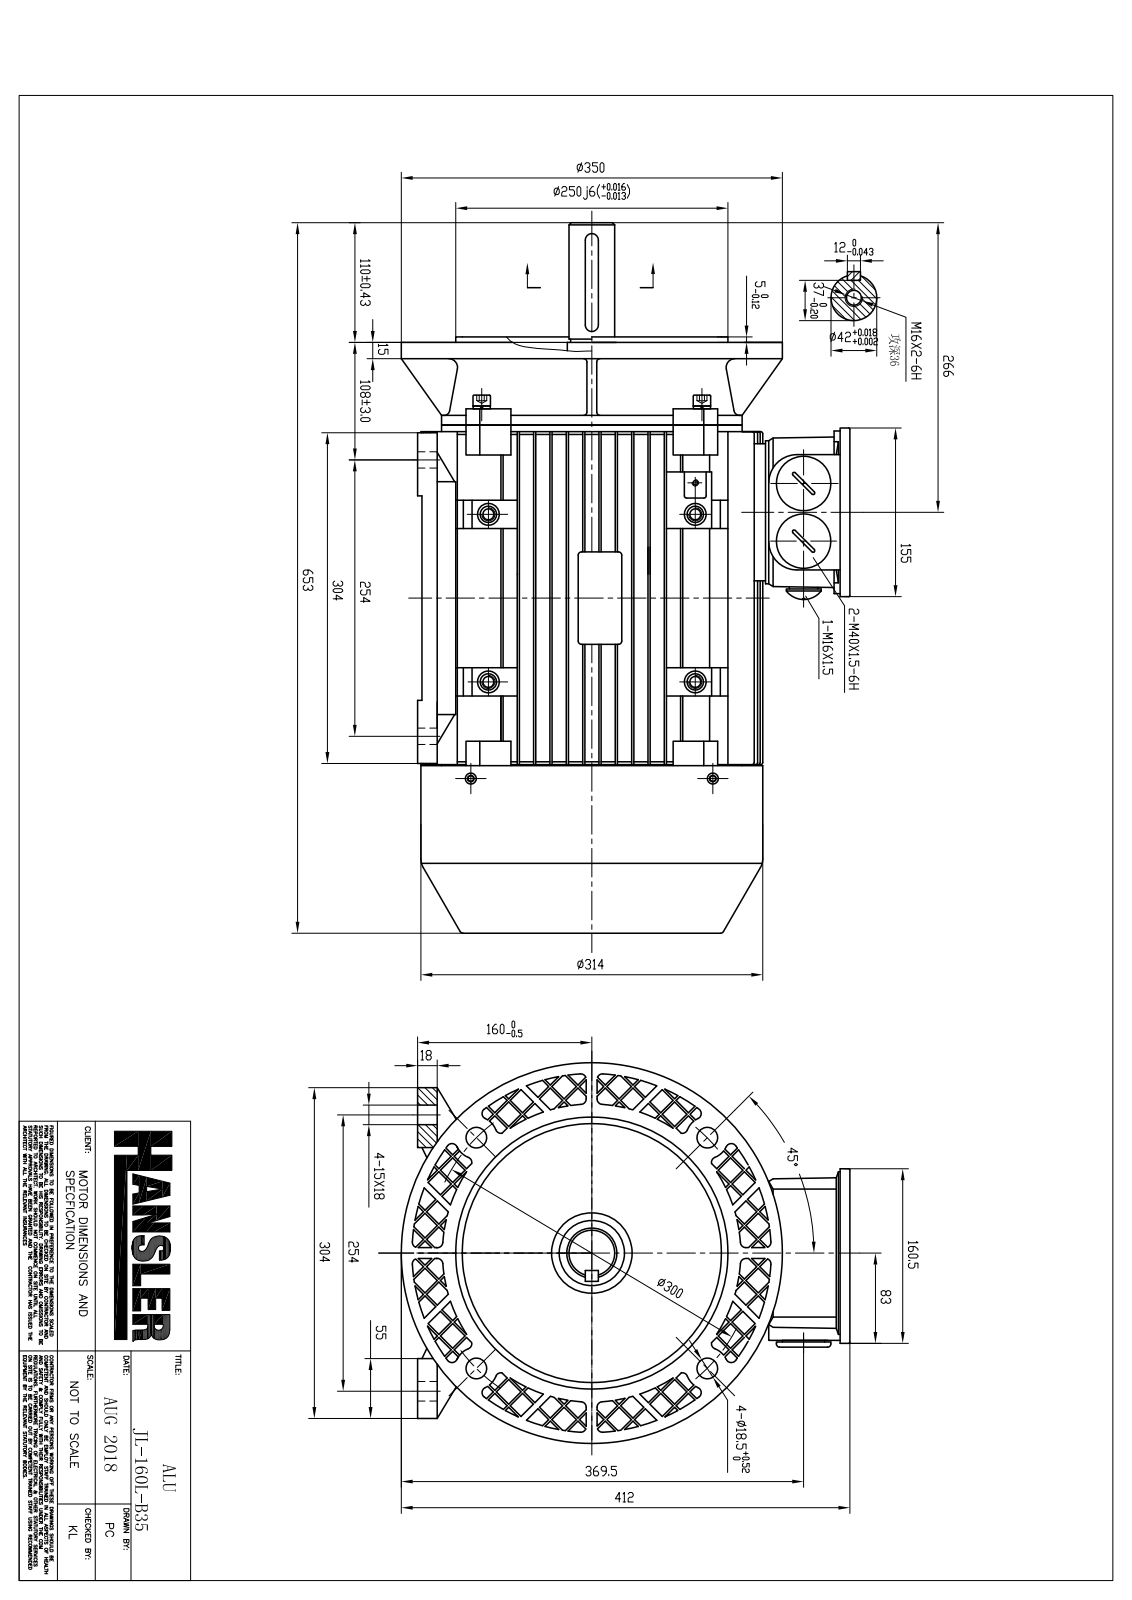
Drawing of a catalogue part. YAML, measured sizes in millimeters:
part_name: "JL-160L-B35"
step_written_by: "SIEMENS PLM Software NX 12.0 (AP203_CONFIGURATION_CONTROLLED_3D_DESIGN_OF_MECHANICAL_PARTS_AND_ASSEMBLIES_MIM_LF)"
units: millimeters
bodies: {solids: 67, faces: 8639, planar: 3998, cylindrical: 2180, other: 2461}
overall_size: [650.92, 417.7, 350]
volume: 7949000
surface_area: 2940000
round_holes:
  - {diameter: 5, count: 28}
  - {diameter: 4.12, count: 12}
  - {diameter: 8.39, count: 8}
  - {diameter: 9.1, count: 8}
  - {diameter: 10, count: 8}
  - {diameter: 12, count: 8}
  - {diameter: 21, count: 8}
  - {diameter: 5.25, count: 5}
  - {diameter: 5.3, count: 5}
  - {diameter: 8, count: 5}
  - {diameter: 16, count: 5}
  - {diameter: 4.2, count: 4}
round_bosses_or_shafts:
  - {diameter: 8, count: 10}
  - {diameter: 5.38, count: 9}
  - {diameter: 15, count: 8}
  - {diameter: 12.59, count: 8}
  - {diameter: 7.19, count: 8}
  - {diameter: 10, count: 5}
  - {diameter: 7.85, count: 5}
  - {diameter: 4.48, count: 5}
partial_cylinders:
  - {radius: 1.2, count: 302}
  - {radius: 1, count: 185}
  - {radius: 2, count: 150}
  - {radius: 4, count: 40}
  - {radius: 1.37, count: 37}
  - {radius: 3, count: 32}
  - {radius: 1.5, count: 26}
  - {radius: 3.42, count: 25}
face_to_face_distances: [15, 30, 2, 45, 90, 13, 17, 75, 60, 105]
hole_center_spacings: [202.36, 207.25, 14.64, 202.24, 207.24, 95.35, 134, 202.23]
